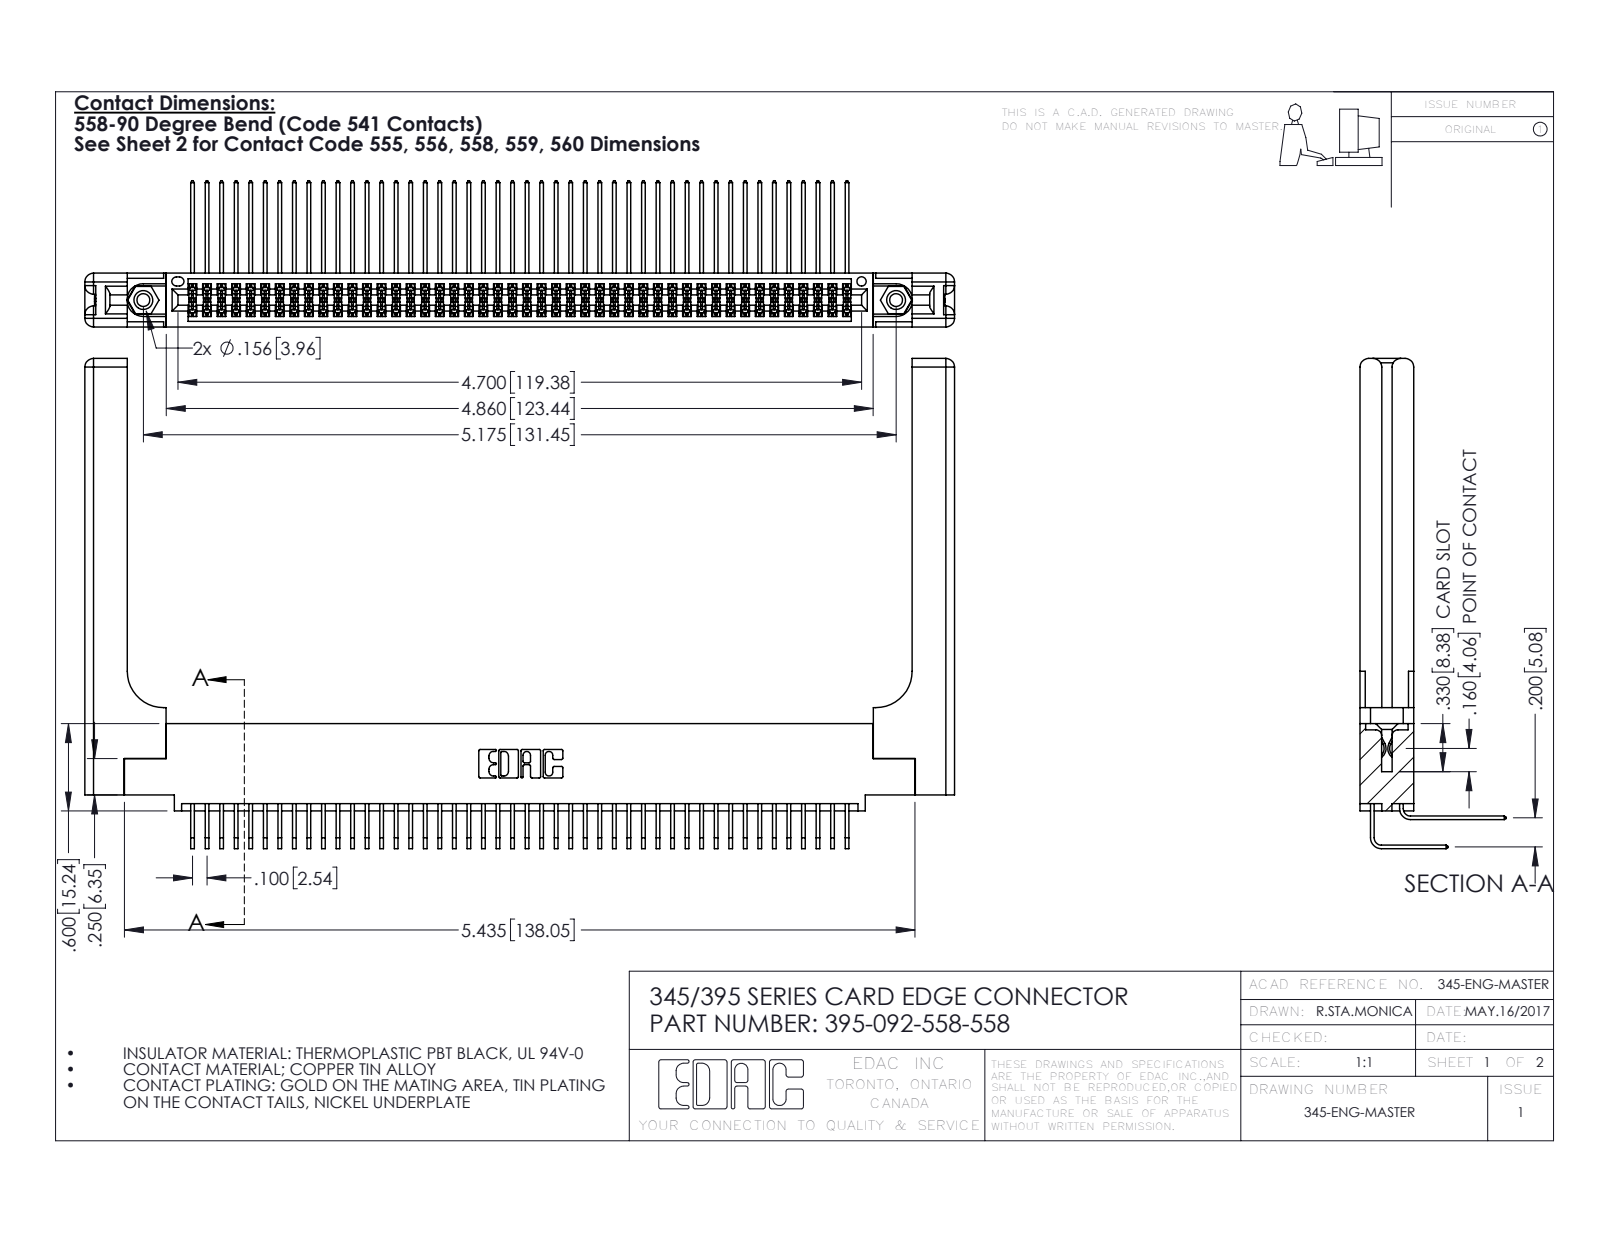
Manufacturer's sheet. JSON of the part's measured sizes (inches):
{"part_name": "345-220-058_345-220-058; 345-292-001_558 559 Tail - 1; 345-292-001_558 Tail - 2; 345-250-001_345-250-001-102 (+2 more)", "step_written_by": "SolidWorks 2016 (CONFIG_CONTROL_DESIGN)", "units": "inches", "bodies": {"solids": 97, "faces": 5170, "planar": 3452, "cylindrical": 1658, "other": 60}, "overall_size": [5.979, 3.369, 1.005], "volume_in3": 1.448, "surface_area_in2": 46.91, "round_holes": [[0.089, 2], [0.125, 2], [0.156, 2], [0.064, 1]], "round_bosses_or_shafts": [[0.155, 2]], "partial_cylinders_radius": [[0.006, 139], [0.01, 22], [0.06, 16], [0.007, 6], [0.031, 6], [0.026, 3], [0.014, 2], [0.019, 2]], "face_to_face_distances": [0.072, 0.298, 0.37, 0.2, 0.098, 0.272, 0.025, 0.225, 0.148, 0.15], "hole_center_spacings": [0.27, 4.939, 5.175]}
